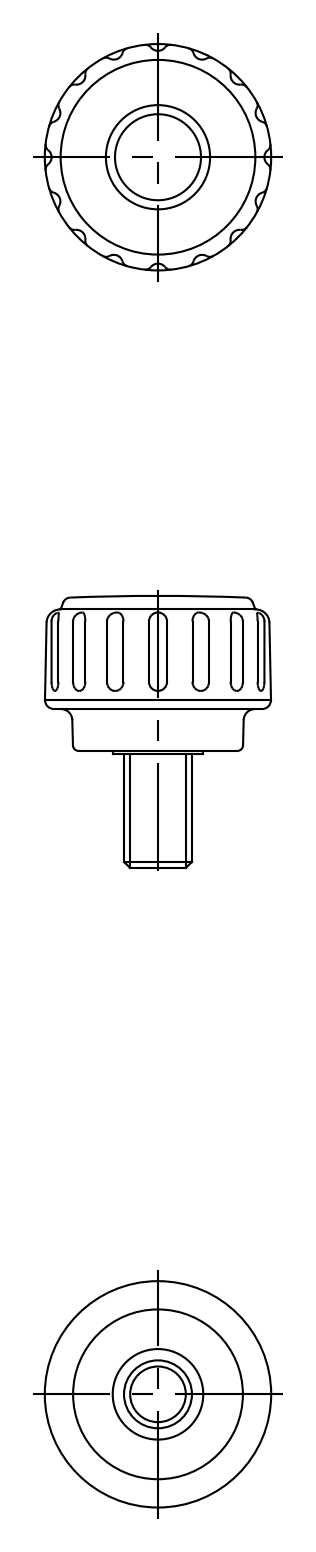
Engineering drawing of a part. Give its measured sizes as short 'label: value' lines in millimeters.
name: screw; knob; KDMS_20_M6_10_WH_23651_36
written by: CADfix (AUTOMOTIVE_DESIGN)
unit: mm
bodies: 2 solids, 70 faces (0 planar, 0 cylindrical, 70 other)
size: 23.95 × 19.97 × 19.97
volume: 3 819 mm³; area: 1 868 mm²
